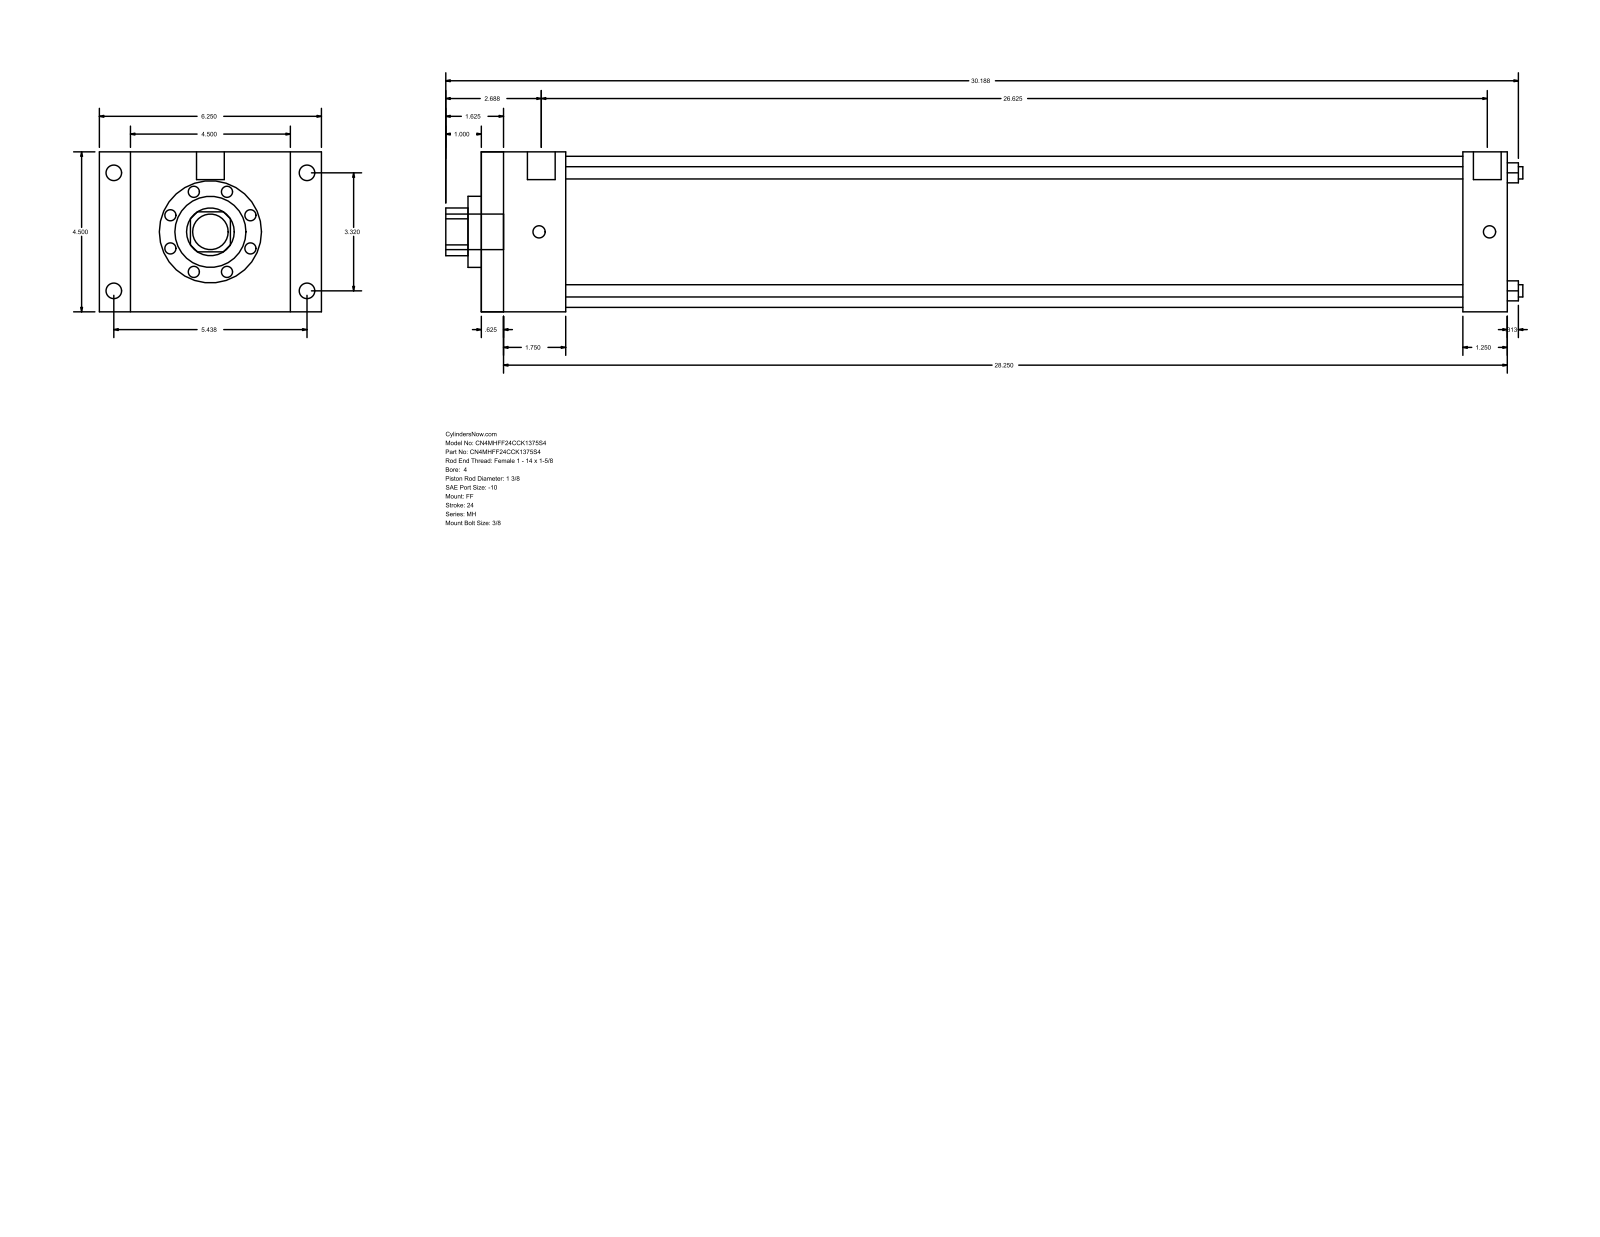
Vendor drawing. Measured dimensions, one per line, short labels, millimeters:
name: MH_FF__0400_1.375
written by: GSSL Pune (CONFIG_CONTROL_DESIGN)
unit: mm
bodies: 0 solids, 92 faces (64 planar, 28 cylindrical, 0 other)
size: 769.94 × 158.75 × 114.3
holes: 4× ⌀8.76, 1× ⌀34.92, 1× ⌀50.8, 1× ⌀107.95
bosses: 4× ⌀11.13, 4× ⌀8.73, 2× ⌀19.84, 1× ⌀25.4
rounds: 1× R17.06
face distances: 114.3, 733.43, 15.87, 717.56, 60.32, 44.45, 673.11, 701.68, 685.81, 641.36
hole spacings: 59.62, 84.32, 119.25
